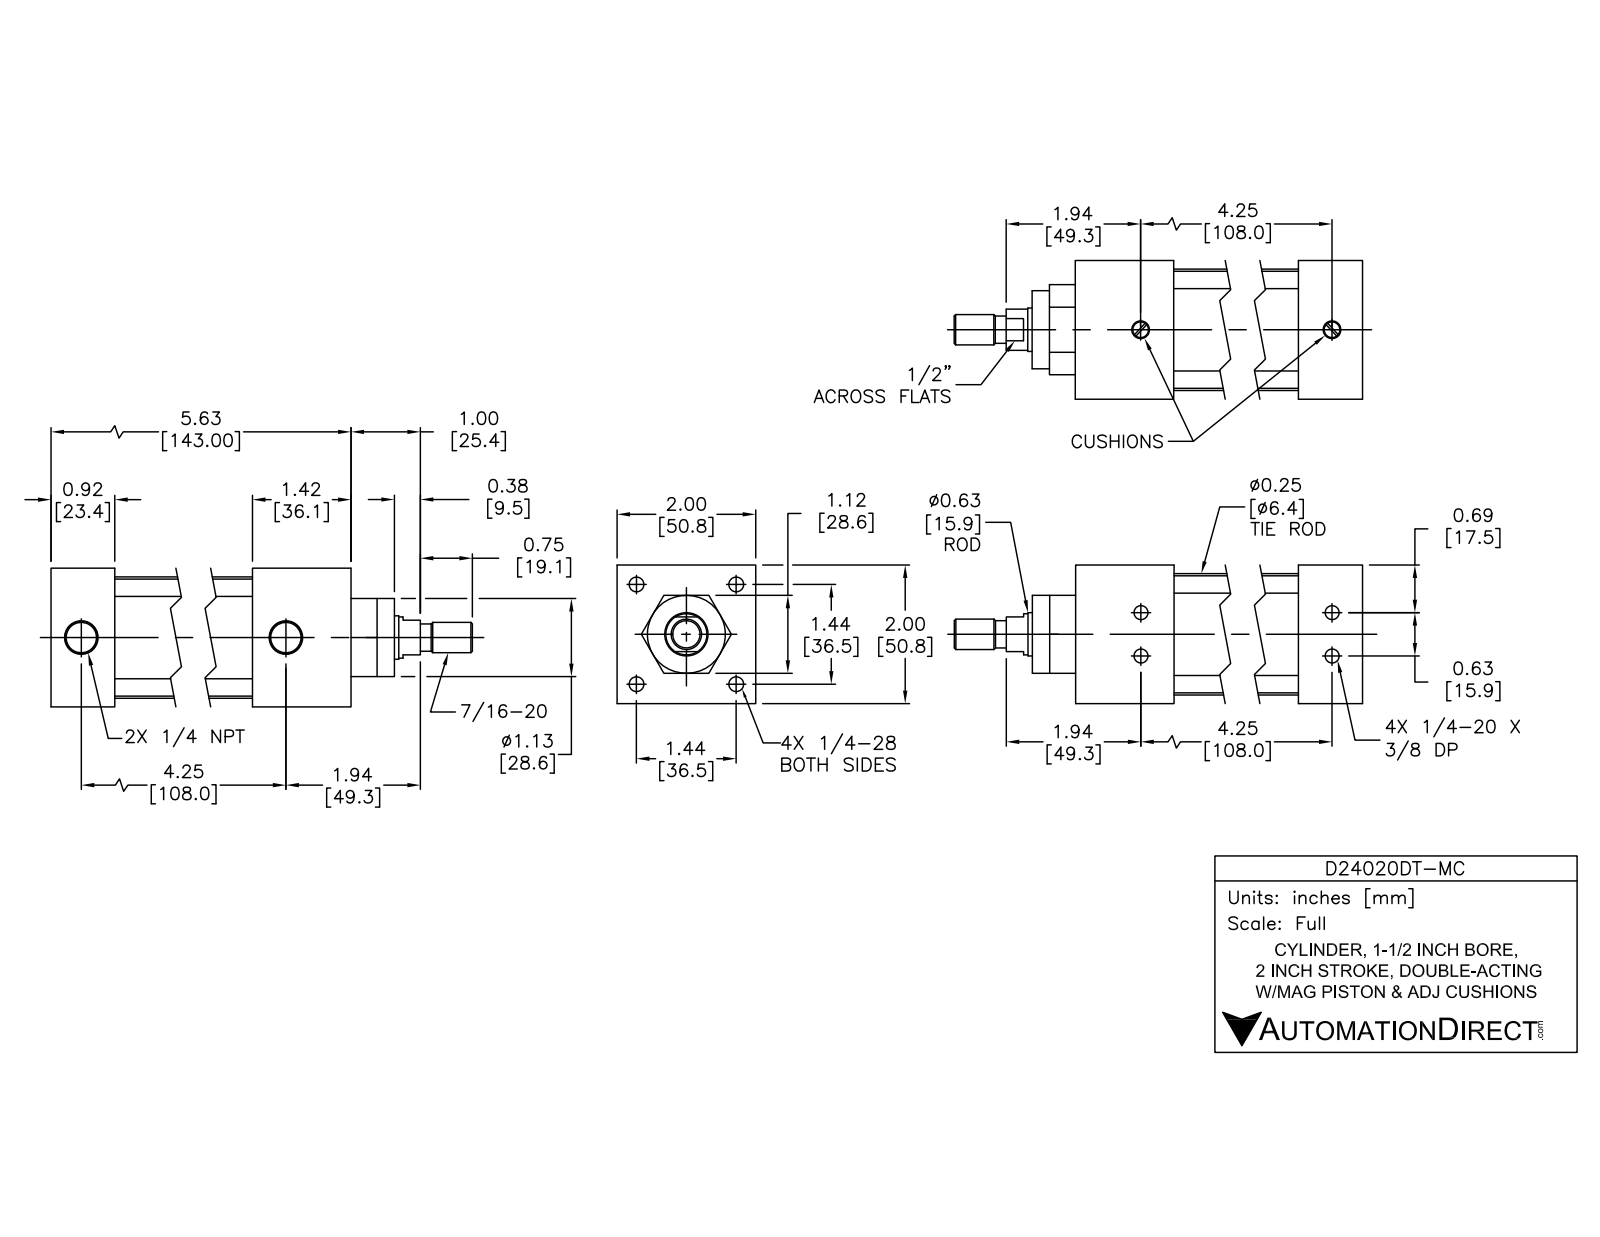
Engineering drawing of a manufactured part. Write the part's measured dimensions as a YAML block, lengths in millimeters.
part_name: "D24020DT-M PISTON; D24020DT-MC; D24020DT-M BODY"
step_written_by: "SolidWorks 2015 (AUTOMOTIVE_DESIGN)"
units: millimeters
bodies: {solids: 12, faces: 303, planar: 99, cylindrical: 114, other: 90}
overall_size: [187.2, 50.8, 50.8]
volume: 243800
surface_area: 79350
round_holes:
  - {diameter: 5, count: 4}
  - {diameter: 5.4, count: 4}
  - {diameter: 7.1, count: 4}
  - {diameter: 10.3, count: 4}
  - {diameter: 7.5, count: 2}
  - {diameter: 12.1, count: 2}
  - {diameter: 15.9, count: 1}
  - {diameter: 16, count: 1}
  - {diameter: 38.1, count: 1}
round_bosses_or_shafts:
  - {diameter: 9.9, count: 4}
  - {diameter: 6.4, count: 4}
  - {diameter: 5.6, count: 4}
  - {diameter: 44.5, count: 1}
  - {diameter: 38, count: 1}
  - {diameter: 28.5, count: 1}
  - {diameter: 15.8, count: 1}
  - {diameter: 15, count: 1}
partial_cylinders:
  - {radius: 5.1, count: 4}
face_to_face_distances: [50.8, 142.8, 36.1, 106.7, 119.4, 83.3, 23.4, 28.5, 116.9, 80.8]
hole_center_spacings: [8, 25.8, 36.4, 15.9, 51.5, 107.9, 108.1, 108.1]
